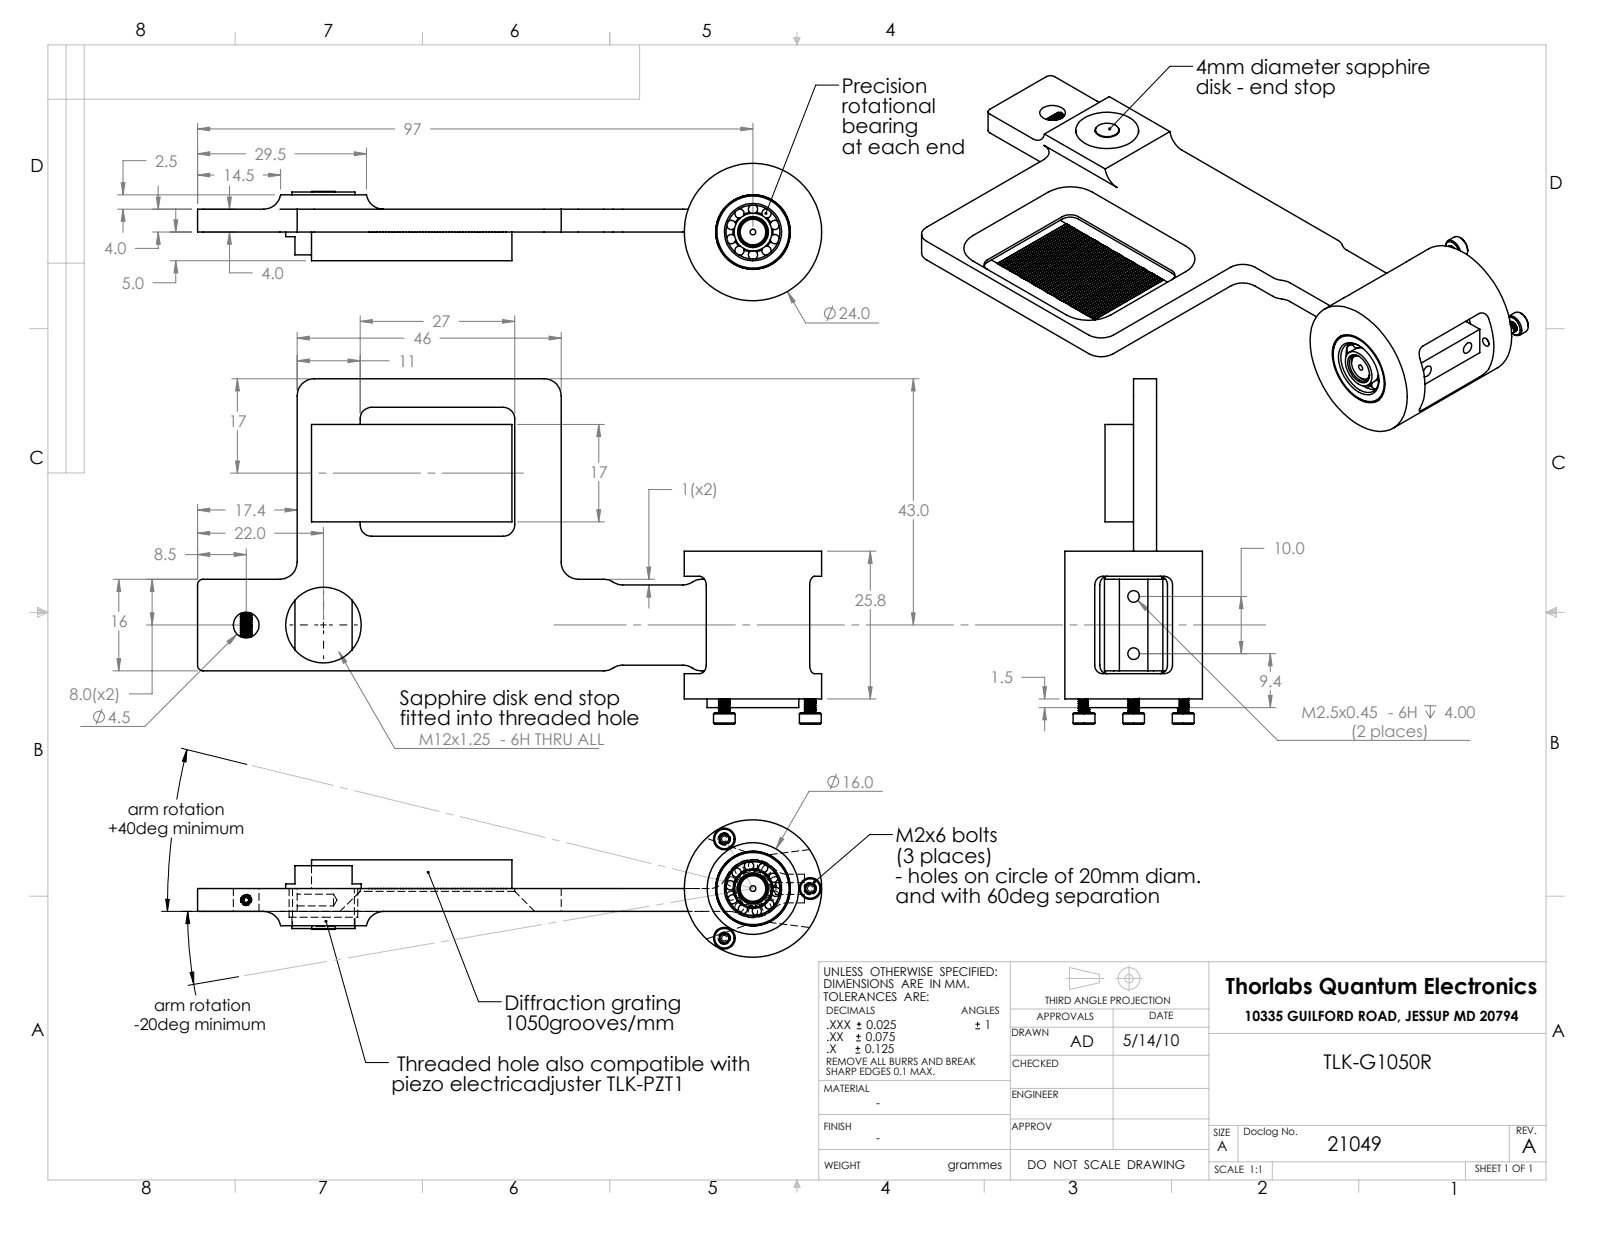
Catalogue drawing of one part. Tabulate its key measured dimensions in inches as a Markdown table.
| quantity | value |
| --- | --- |
| part name | 21049-E0W |
| STEP written by | SolidWorks 2009 (AUTOMOTIVE_DESIGN) |
| units | inches |
| bodies | 0 solids, 639 faces (151 planar, 320 cylindrical, 168 other) |
| overall size | 4.291 × 2.374 × 0.945 |
| round holes (diameter × count) | 0.081 × 3, 0.063 × 2, 0.087 × 2, 0.039 × 1, 0.165 × 1, 0.177 × 1, 0.197 × 1, 0.37 × 1, 0.513 × 1 |
| round bosses / shafts (diameter × count) | 0.067 × 10, 0.079 × 4, 0.15 × 3, 0.058 × 3, 0.945 × 1, 0.63 × 1, 0.52 × 1, 0.433 × 1 |
| partial cylindrical surfaces (radius × count) | 0.118 × 18, 0.059 × 8, 0.079 × 4, 0.039 × 2, 0.033 × 1, 0.201 × 1 |
| main face-to-face distances | 0.157, 0.197, 0.354, 0.823, 0.193, 0.098, 0.02, 0.669, 0.173, 0.843 |
| hole center spacings | 0.394, 0.682, 0.531, 0.919, 1.311, 3.298, 3.314, 3.485 |
